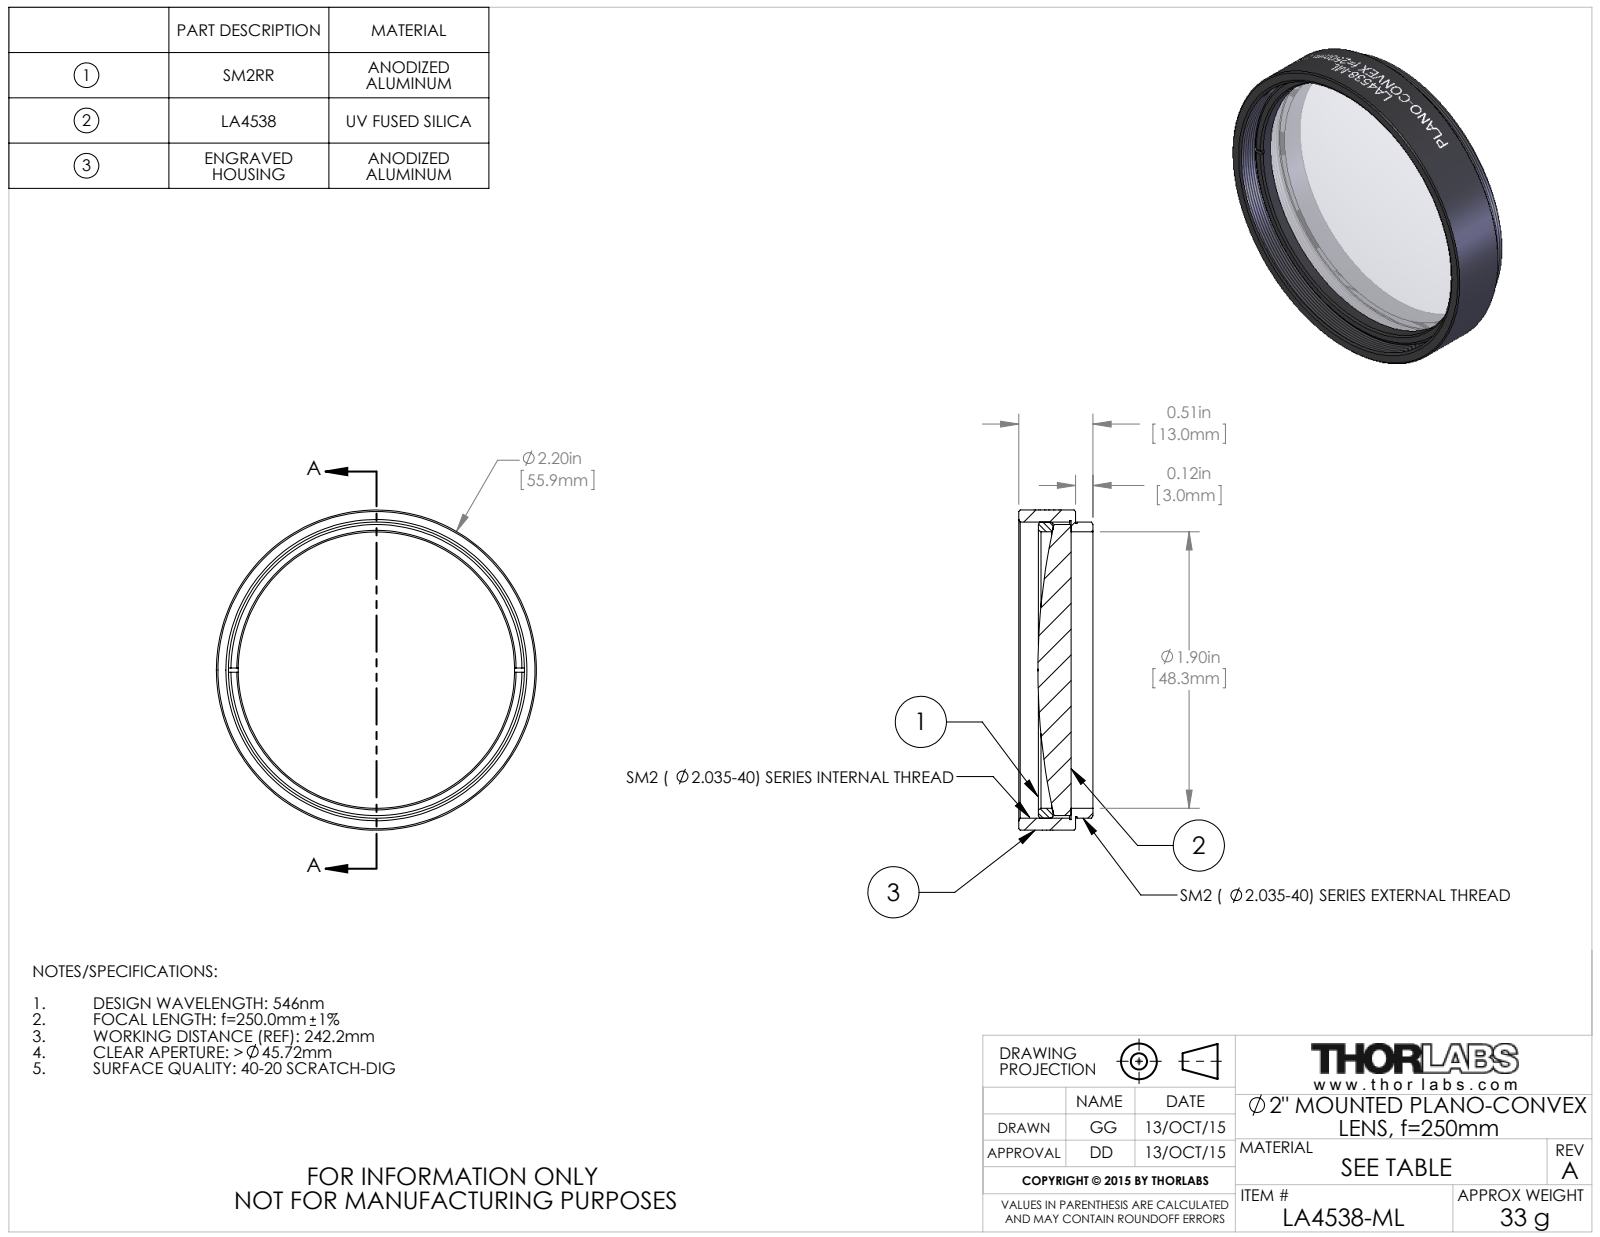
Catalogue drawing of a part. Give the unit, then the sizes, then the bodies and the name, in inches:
Units: inches
Overall size (bounding box): 2.2 × 2.2 × 0.51
Round holes (diameter × count): ⌀1.9 ×1, ⌀2.055 ×1
Round bosses / shafts (diameter × count): ⌀2.2 ×1, ⌀2.035 ×1, ⌀2.015 ×1, ⌀2 ×1
Main face-to-face distances: 0.03, 0.39, 0.36, 0.12, 0.15, 0.51, 0.276, 0.156, 0.126, 0.235
Volume: 0.859 in³ · Surface area: 17.6 in²
Bodies: 3 solids, 113 faces (16 planar, 73 cylindrical, 24 other)
Part name (STEP PRODUCT): TTN039289-E0W
STEP written by: SolidWorks 2014 (CONFIG_CONTROL_DESIGN)
